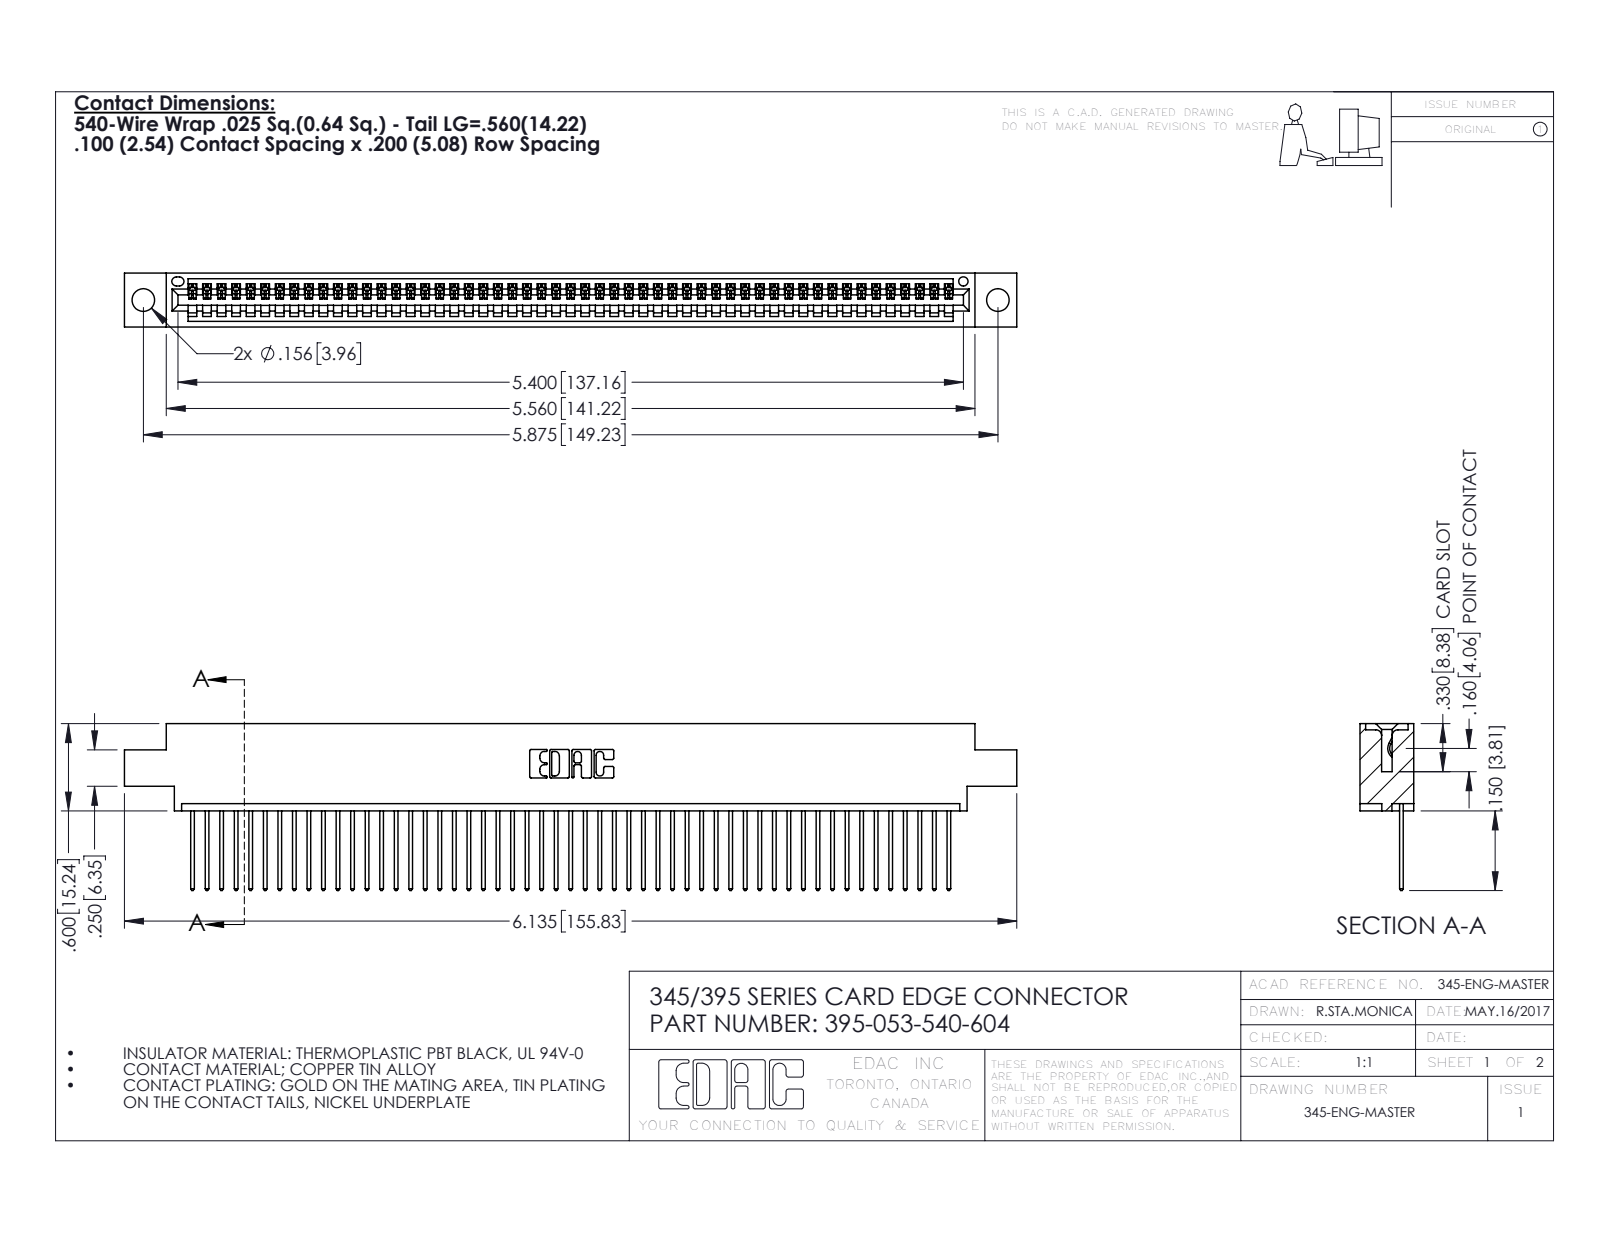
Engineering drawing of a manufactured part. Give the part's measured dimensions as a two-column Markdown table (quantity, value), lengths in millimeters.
| quantity | value |
| --- | --- |
| part name | 345 Part_0.170 Offset - 0.156 Dia-TH; 395-053-540-604; 345-292-001_345-293-140 |
| STEP written by | SolidWorks 2016 (CONFIG_CONTROL_DESIGN) |
| units | millimeters |
| bodies | 54 solids, 3204 faces (2204 planar, 1000 cylindrical, 0 other) |
| overall size | 155.8 × 29.1 × 9.4 |
| volume | 14 800 mm³ |
| surface area | 20 220 mm² |
| round holes (diameter × count) | 4 × 2, 1.6 × 1 |
| partial cylindrical surfaces (radius × count) | 0.2 × 106, 0.3 × 106, 0.3 × 22, 0.2 × 6, 0.8 × 6, 0.7 × 3, 0.8 × 2, 1 × 2 |
| main face-to-face distances | 7.6, 1.8, 9.4, 2.5, 6.9, 0.6, 5.1, 5.7, 4.4, 3.8 |
| hole center spacings | 6.9, 143.2, 149.2 |
